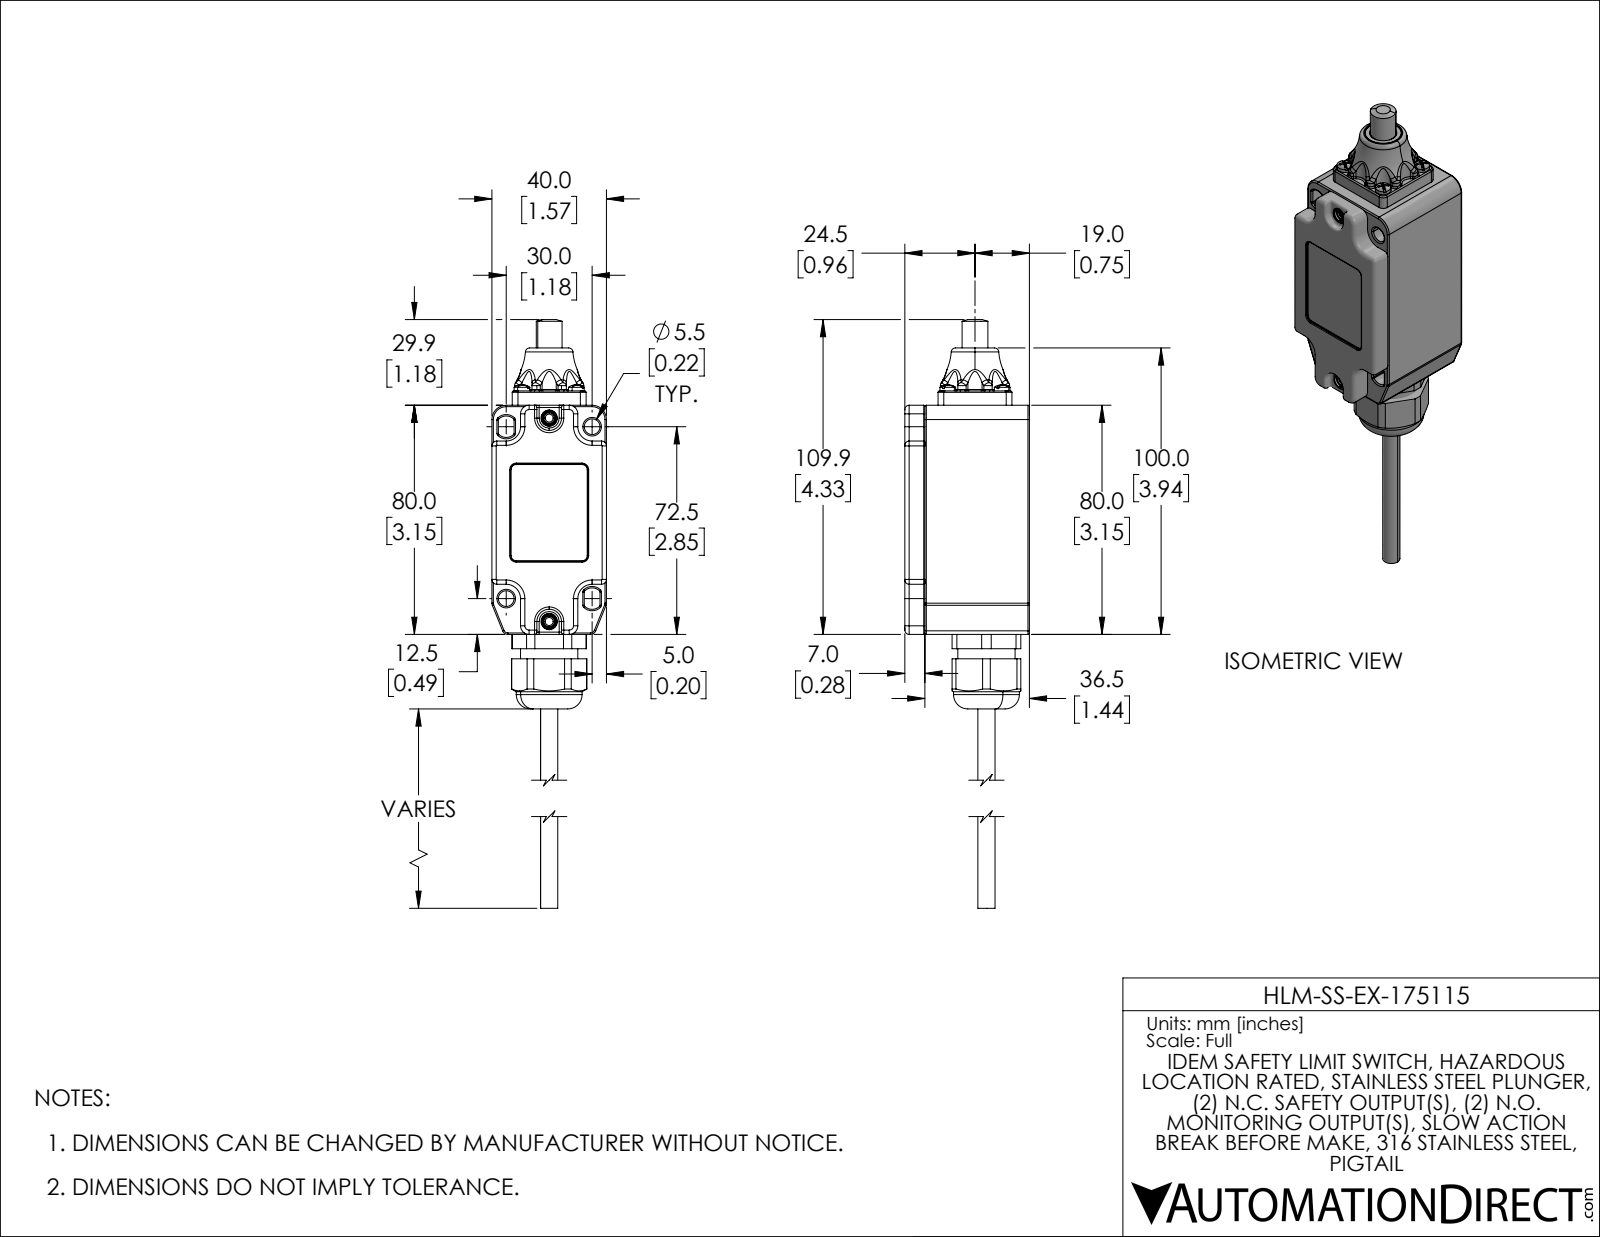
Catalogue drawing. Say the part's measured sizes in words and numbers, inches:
The part is named "HLM-SS-EX-175115". Its 3-D file was written by "SolidWorks 2021 (AUTOMOTIVE_DESIGN)". It is 16 solids with 1836 faces: 468 planar, 479 cylindrical and 889 other. Overall it measures 7.634 by 1.732 by 1.638 inches. Its volume is 4.581 cubic inches and its surface area 78.61 square inches. Round holes: 10 of diameter 0.102, 4 of diameter 0.13, 2 of diameter 0.134, 2 of diameter 0.157, 2 of diameter 0.169, 2 of diameter 0.217, 2 of diameter 0.512, 1 of diameter 0.114, 1 of diameter 0.173, 1 of diameter 0.22, 1 of diameter 0.272, 1 of diameter 0.276. Round bosses or shafts: 7 of diameter 0.236, 4 of diameter 0.216, 4 of diameter 0.118, 2 of diameter 0.276, 2 of diameter 0.051, 1 of diameter 0.937, 1 of diameter 0.89, 1 of diameter 0.787. Partial cylindrical surfaces (rounded edges, fillets, slot ends): 122 of radius 0.02, 24 of radius 0.016, 16 of radius 0.079, 14 of radius 0.006, 13 of radius 0.039, 12 of radius 0.067, 12 of radius 0.138, 10 of radius 0.031. The main face-to-face distances are 0.12, 1.518, 1.398, 1.638, 1.732, 0.098, 0.236, 1.634, 1.496, 0.087. The hole center spacings are 0.748, 0.529, 0.354, 0.432, 0.65, 0.75, 0.828, 0.854.
